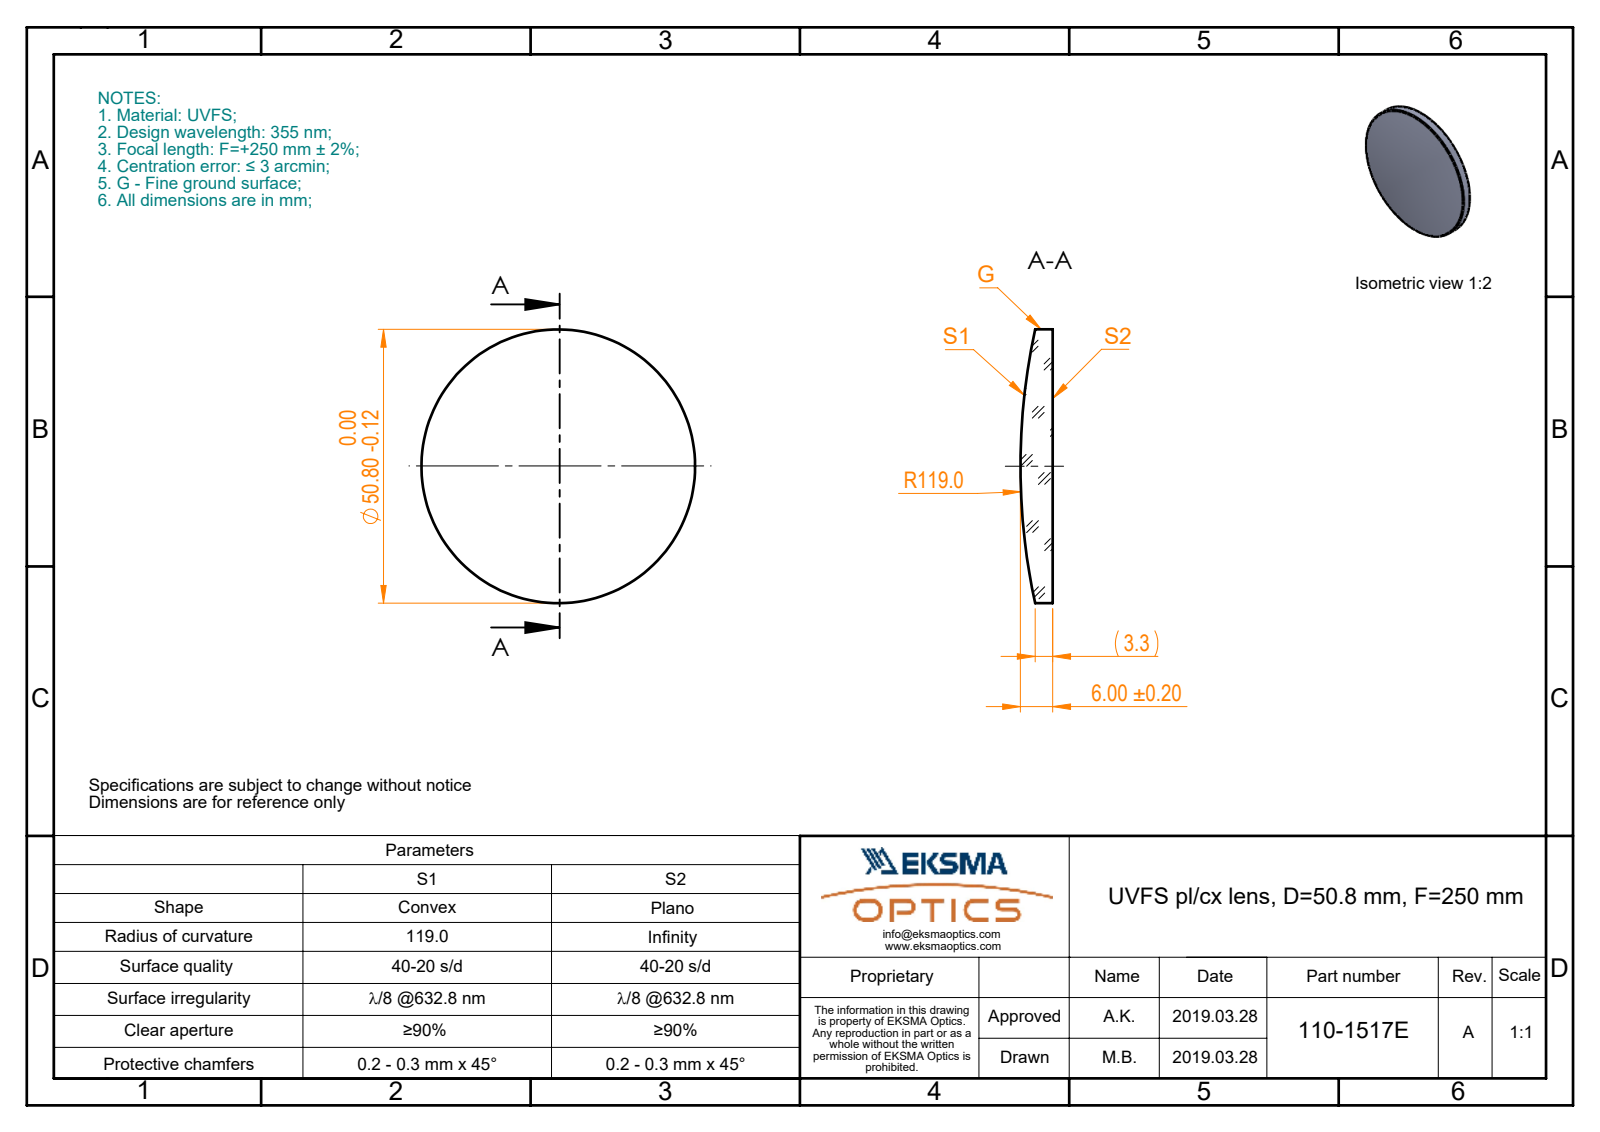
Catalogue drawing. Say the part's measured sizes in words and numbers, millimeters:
The part is named "110-1517E UVFS pl-cx 50.8 F250". Its 3-D file was written by "SolidWorks 2017 (CONFIG_CONTROL_DESIGN)". It is 1 solid with 5 faces: 1 planar, 2 cylindrical and 2 other. Overall it measures 50.8 by 50.8 by 6 millimeters. Its volume is 9 393 cubic millimeters and its surface area 4 597 square millimeters. Round bosses or shafts: 1 of diameter 50.8.
